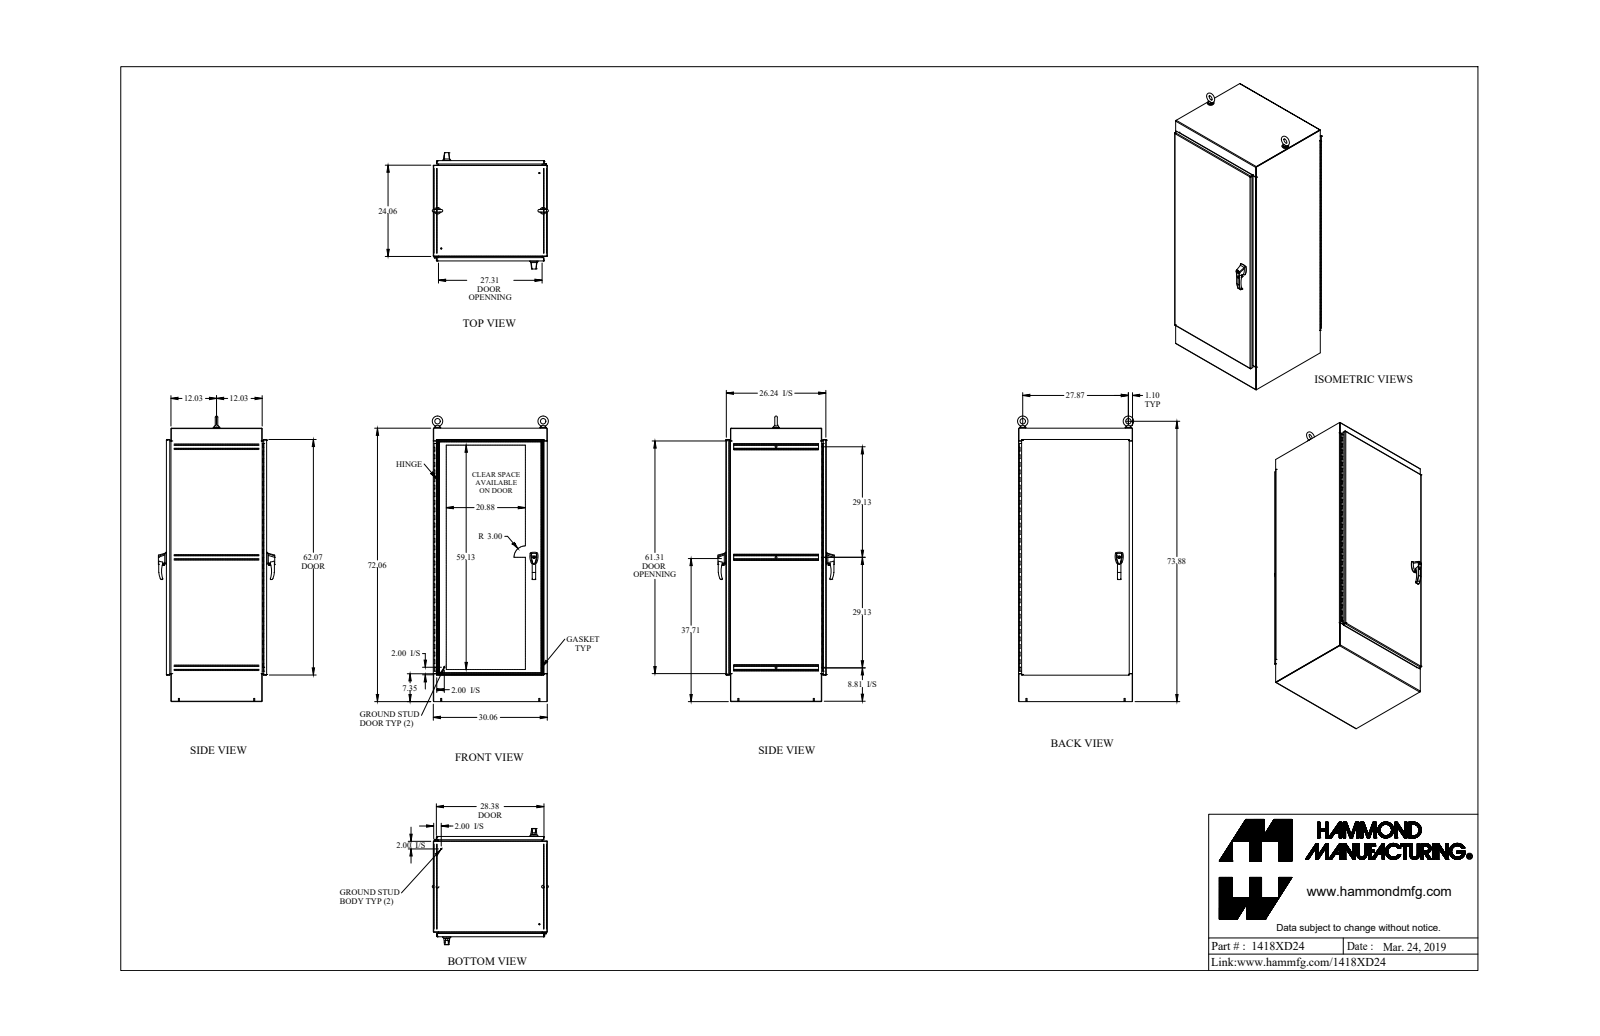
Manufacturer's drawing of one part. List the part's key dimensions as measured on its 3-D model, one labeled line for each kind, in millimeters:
Part name (STEP PRODUCT): 1418XD24_Default
STEP written by: SolidWorks 2019 (CONFIG_CONTROL_DESIGN)
Units: millimetres
Bodies: 83 solids, 3052 faces (1358 planar, 1428 cylindrical, 266 other)
Overall size (bounding box): 1923.1 × 790.4 × 778.9
Volume: 18 480 000 mm³ · Surface area: 15 360 000 mm²
Round holes (diameter × count): ⌀7.7 ×20, ⌀6.4 ×4, ⌀6.5 ×4, ⌀7.1 ×4, ⌀7.1 ×4, ⌀8 ×4, ⌀9.9 ×4, ⌀10.5 ×4, ⌀12.7 ×3, ⌀2.8 ×2, ⌀4.4 ×2, ⌀5.9 ×2
Round bosses / shafts (diameter × count): ⌀7.1 ×8, ⌀25.4 ×4, ⌀19.1 ×4, ⌀16 ×4, ⌀15.9 ×4, ⌀11.2 ×4, ⌀9.4 ×4, ⌀6.4 ×4
Partial cylindrical surfaces — rounded edges, fillets, slot ends (radius × count): R3.2 ×44, R1.1 ×42, R3.5 ×36, R0.5 ×32, R1.2 ×24, R3.6 ×24, R1.5 ×16, R0.8 ×12
Main face-to-face distances: 2.4, 669, 761.1, 758.7, 30.1, 638.9, 666.6, 671.4, 763.5, 1827.9
Hole centre spacings: 152.4, 735.6, 304.8, 781.5, 457.2, 852.6, 609.6, 943.1
